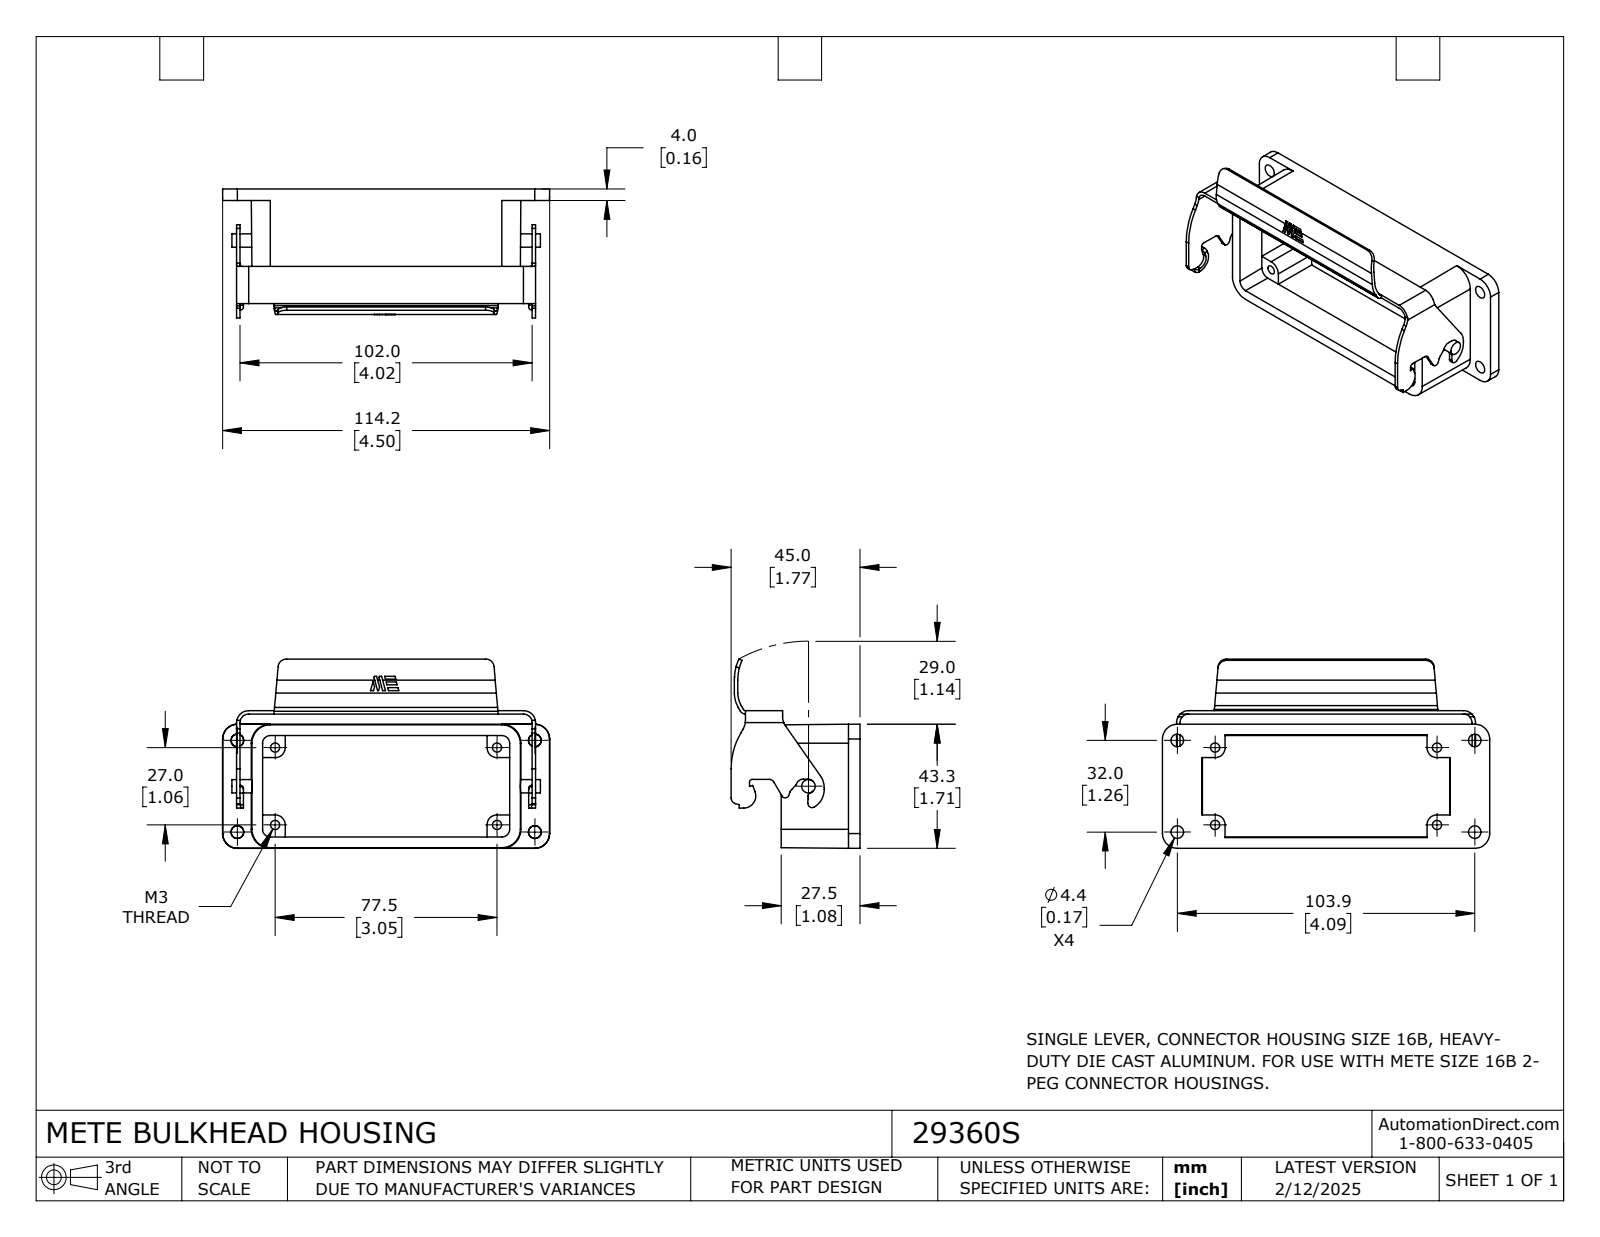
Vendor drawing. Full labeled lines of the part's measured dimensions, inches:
Part name (STEP PRODUCT): 29360S
STEP written by: SolidWorks 2024 (CONFIG_CONTROL_DESIGN)
Units: inches
Bodies: 1 solid, 209 faces (118 planar, 71 cylindrical, 20 other)
Overall size (bounding box): 4.498 × 2.601 × 1.772
Volume: 2.283 in³ · Surface area: 43.24 in²
Round holes (diameter × count): ⌀0.126 ×4
Round bosses / shafts (diameter × count): ⌀0.185 ×1
Partial cylindrical surfaces — rounded edges, fillets, slot ends (radius × count): R0.039 ×6, R0.118 ×5, R0.138 ×4, R0.079 ×3, R0.098 ×3, R0.165 ×3, R0.236 ×2, R0.276 ×2
Main face-to-face distances: 0.047, 4.063, 0.335, 1.744, 0.287, 1.697, 1.409, 1.083, 0.925, 0.157
Hole centre spacings: 1.063, 3.051, 3.231
